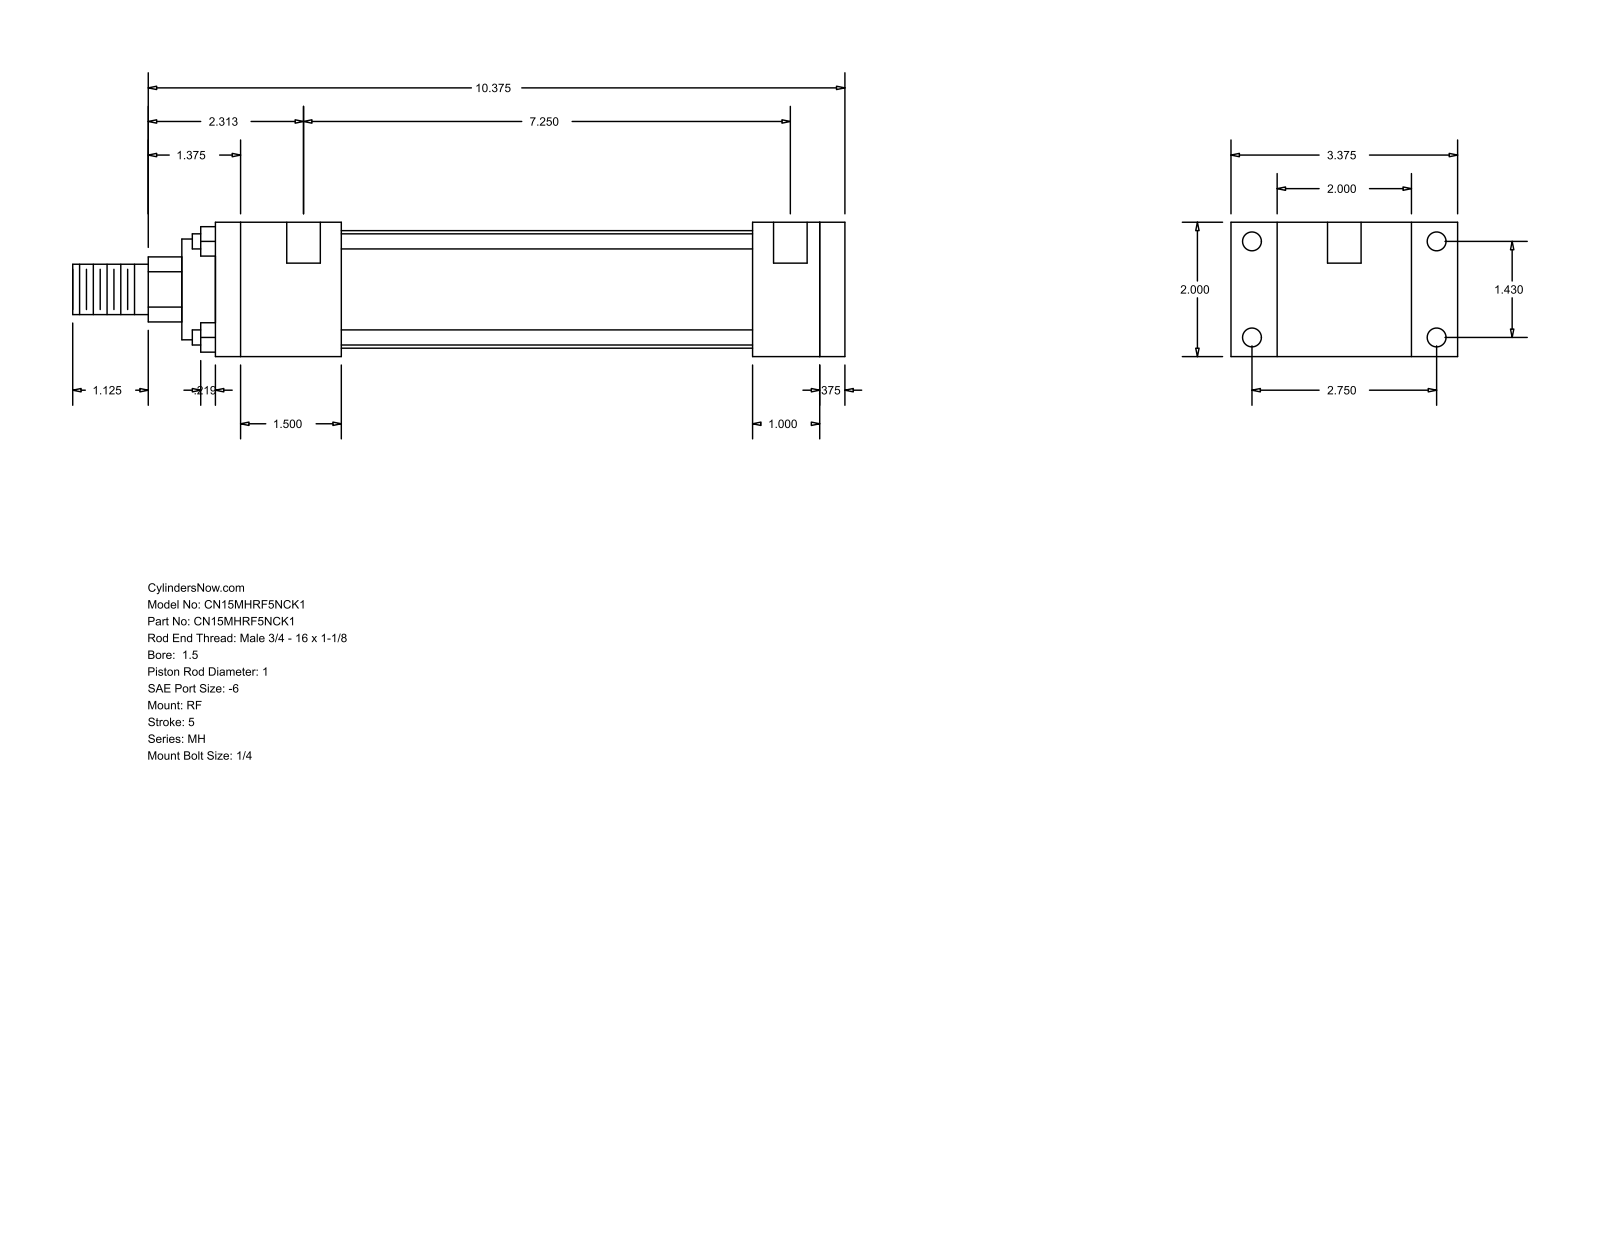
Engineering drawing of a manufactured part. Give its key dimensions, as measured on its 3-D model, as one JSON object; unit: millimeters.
{"part_name": "MH_RF__0150_1", "step_written_by": "GSSL Pune (CONFIG_CONTROL_DESIGN)", "units": "millimeters", "bodies": {"solids": 0, "faces": 92, "planar": 64, "cylindrical": 28, "other": 0}, "overall_size": [292.1, 85.72, 50.8], "round_holes": [[5.56, 4], [7.14, 4], [12.7, 2]], "round_bosses_or_shafts": [[5.71, 4], [44.45, 1], [38.1, 1], [25.4, 1], [19.05, 1]], "partial_cylinders_radius": [[12.29, 1]], "face_to_face_distances": [50.8, 9.52, 228.6, 25.4, 238.12, 17.46, 68.26, 203.2, 34.92, 47.63], "hole_center_spacings": [36.32, 69.84, 78.72, 187.33, 3.18, 184.15]}
